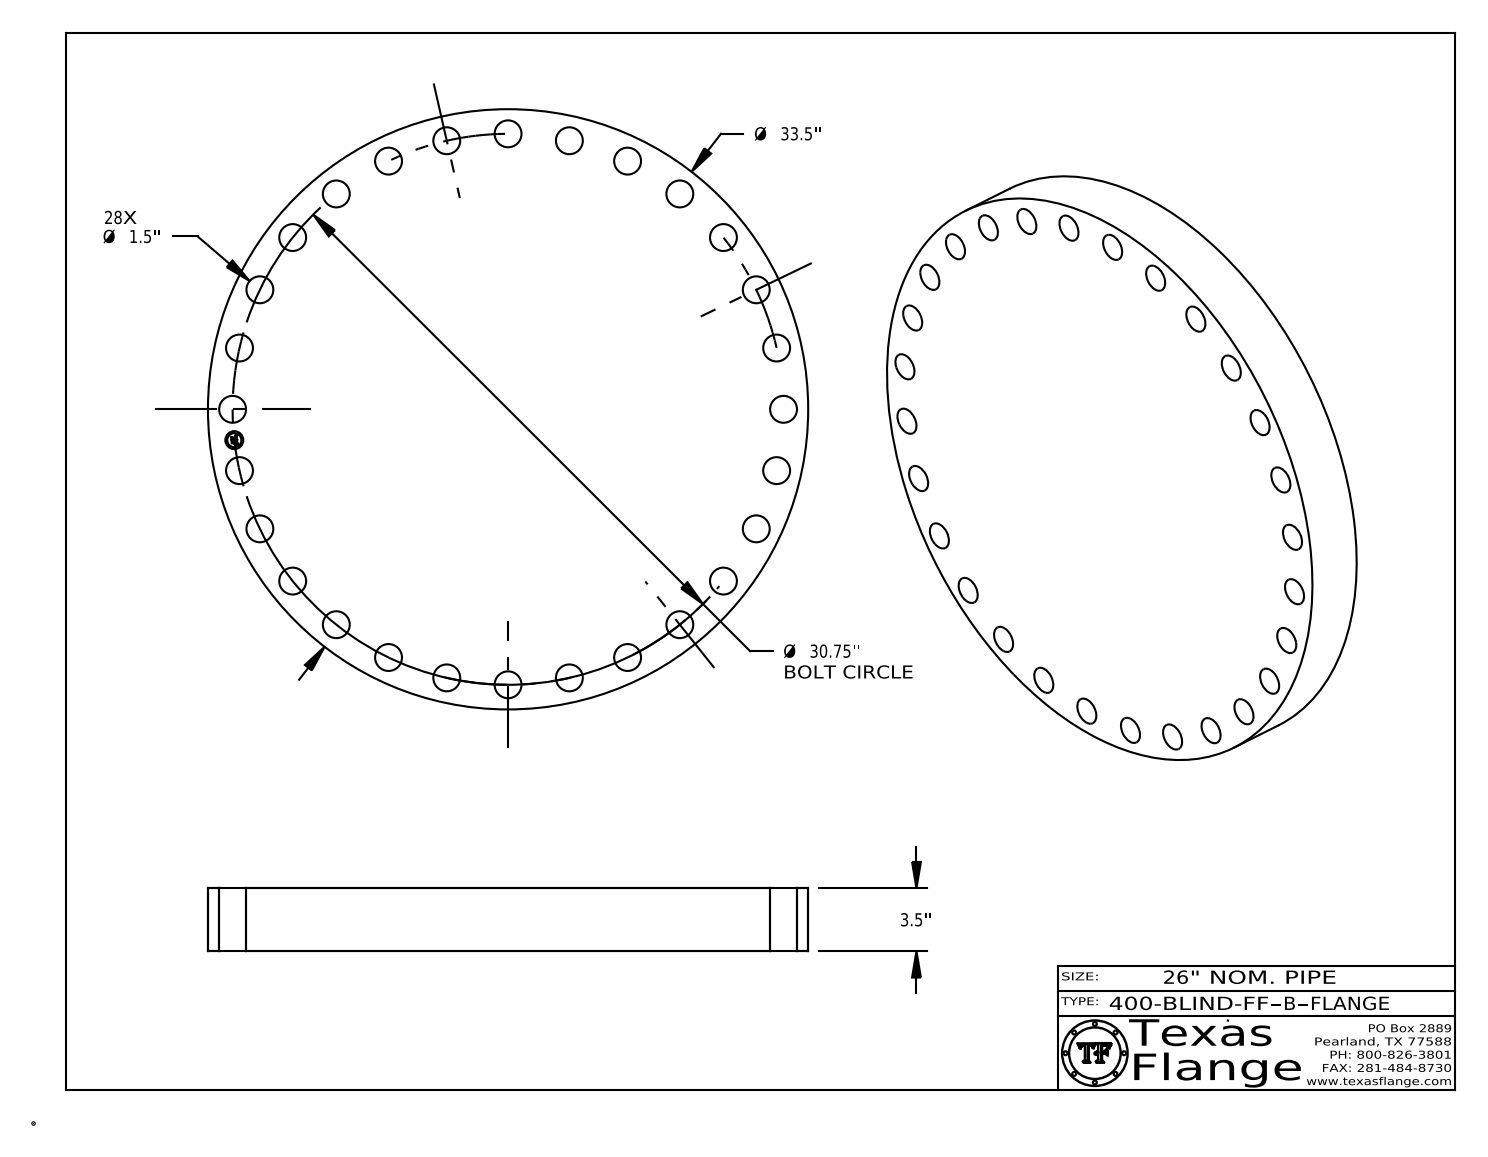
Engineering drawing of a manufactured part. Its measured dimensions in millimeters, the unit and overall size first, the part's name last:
Units: millimetres
Overall size (bounding box): 850.9 × 850.9 × 88.9
Round holes (diameter × count): ⌀38.1 ×28, ⌀25.4 ×1
Round bosses / shafts (diameter × count): ⌀1.5 ×8, ⌀850.9 ×1, ⌀20 ×1
Main face-to-face distances: 88.9, 88.5, 0.4, 7.6, 7.4, 1.4, 4.9, 6.3, 0.3, 1.1
Hole centre spacings: 173.8, 737.2, 552.3, 338.9, 415.5, 487, 661.3, 761.5
Volume: 47 720 000 mm³ · Surface area: 1 609 000 mm²
Bodies: 1 solid, 445 faces (367 planar, 78 cylindrical, 0 other)
Part name (STEP PRODUCT): 400-BLIND-FF, Series B
STEP written by: CATIA V5 STEP AP214 (AUTOMOTIVE_DESIGN)
